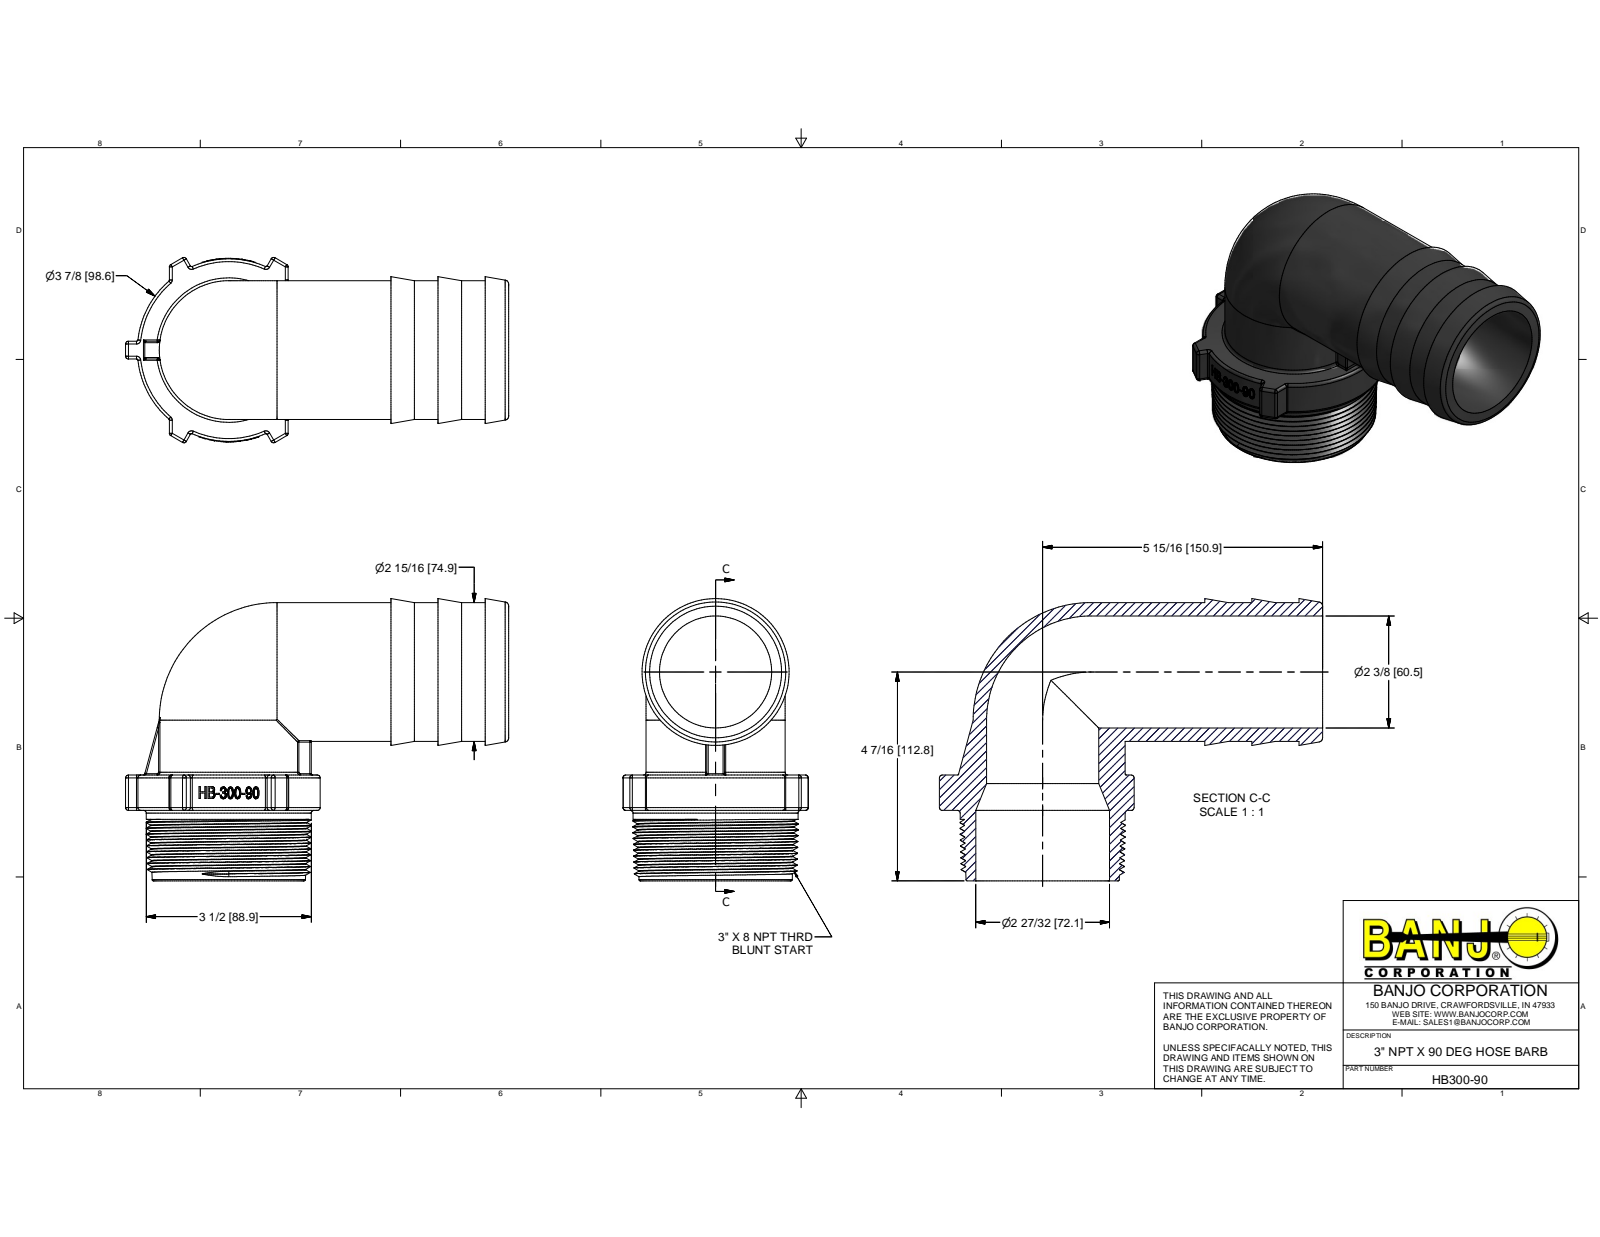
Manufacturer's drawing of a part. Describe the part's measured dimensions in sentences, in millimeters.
The part is named "HB300-90". Its 3-D file was written by "Autodesk Inventor 2014 (AUTOMOTIVE_DESIGN)". It is 1 solid with 580 faces: 179 planar, 128 cylindrical and 273 other. Overall it measures 206.5 by 152.4 by 100.06 millimeters. Its volume is 467 663 cubic millimeters and its surface area 129 433 square millimeters. Round holes: 2 of diameter 60.45, 1 of diameter 72.14. Round bosses or shafts: 2 of diameter 74.93, 1 of diameter 88.9. Partial cylindrical surfaces (rounded edges, fillets, slot ends): 36 of radius 1.52, 24 of radius 0.76, 1 of radius 23.12, 1 of radius 49.28, 1 of radius 49.53. The main face-to-face distances are 38.1, 57.15, 25.4, 19.05, 50.8, 63.5, 12.7, 33.28, 4.82, 23.87.
